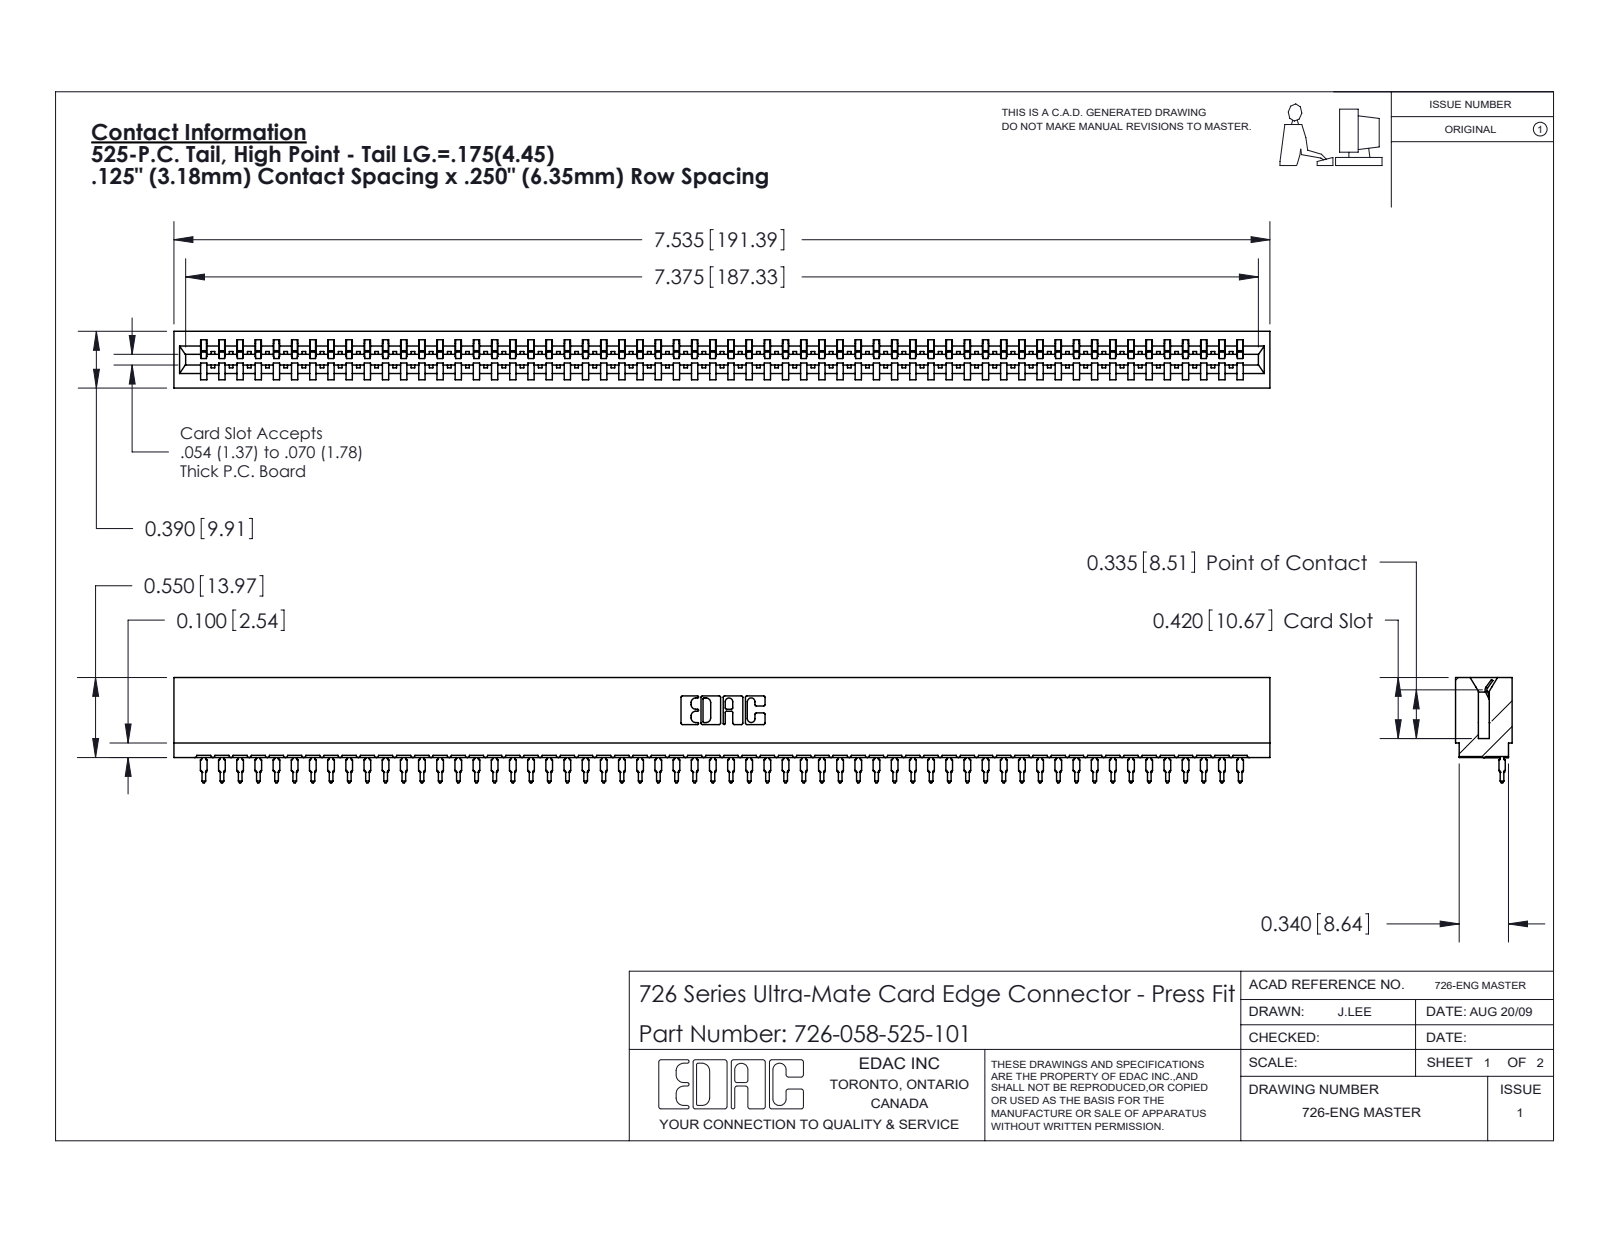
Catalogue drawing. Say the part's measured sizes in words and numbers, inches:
The part is named "746-292-001_525; 726-058-525-101; 726 Part_.515 Slot Depth - 01". Its 3-D file was written by "SolidWorks 2020 (CONFIG_CONTROL_DESIGN)". It is 59 solids with 6361 faces: 3709 planar, 1144 cylindrical and 1508 other. Overall it measures 7.535 by 0.724 by 0.39 inches. Its volume is 1.033 cubic inches and its surface area 39.98 square inches. Partial cylindrical surfaces (rounded edges, fillets, slot ends): 116 of radius 0.021, 59 of radius 0.015, 22 of radius 0.01, 6 of radius 0.007, 6 of radius 0.031, 4 of radius 0.005, 4 of radius 0.011, 3 of radius 0.026. The main face-to-face distances are 0.057, 0.333, 0.39, 0.025, 0.307, 0.275, 0.365, 0.032, 0.174, 0.232.
